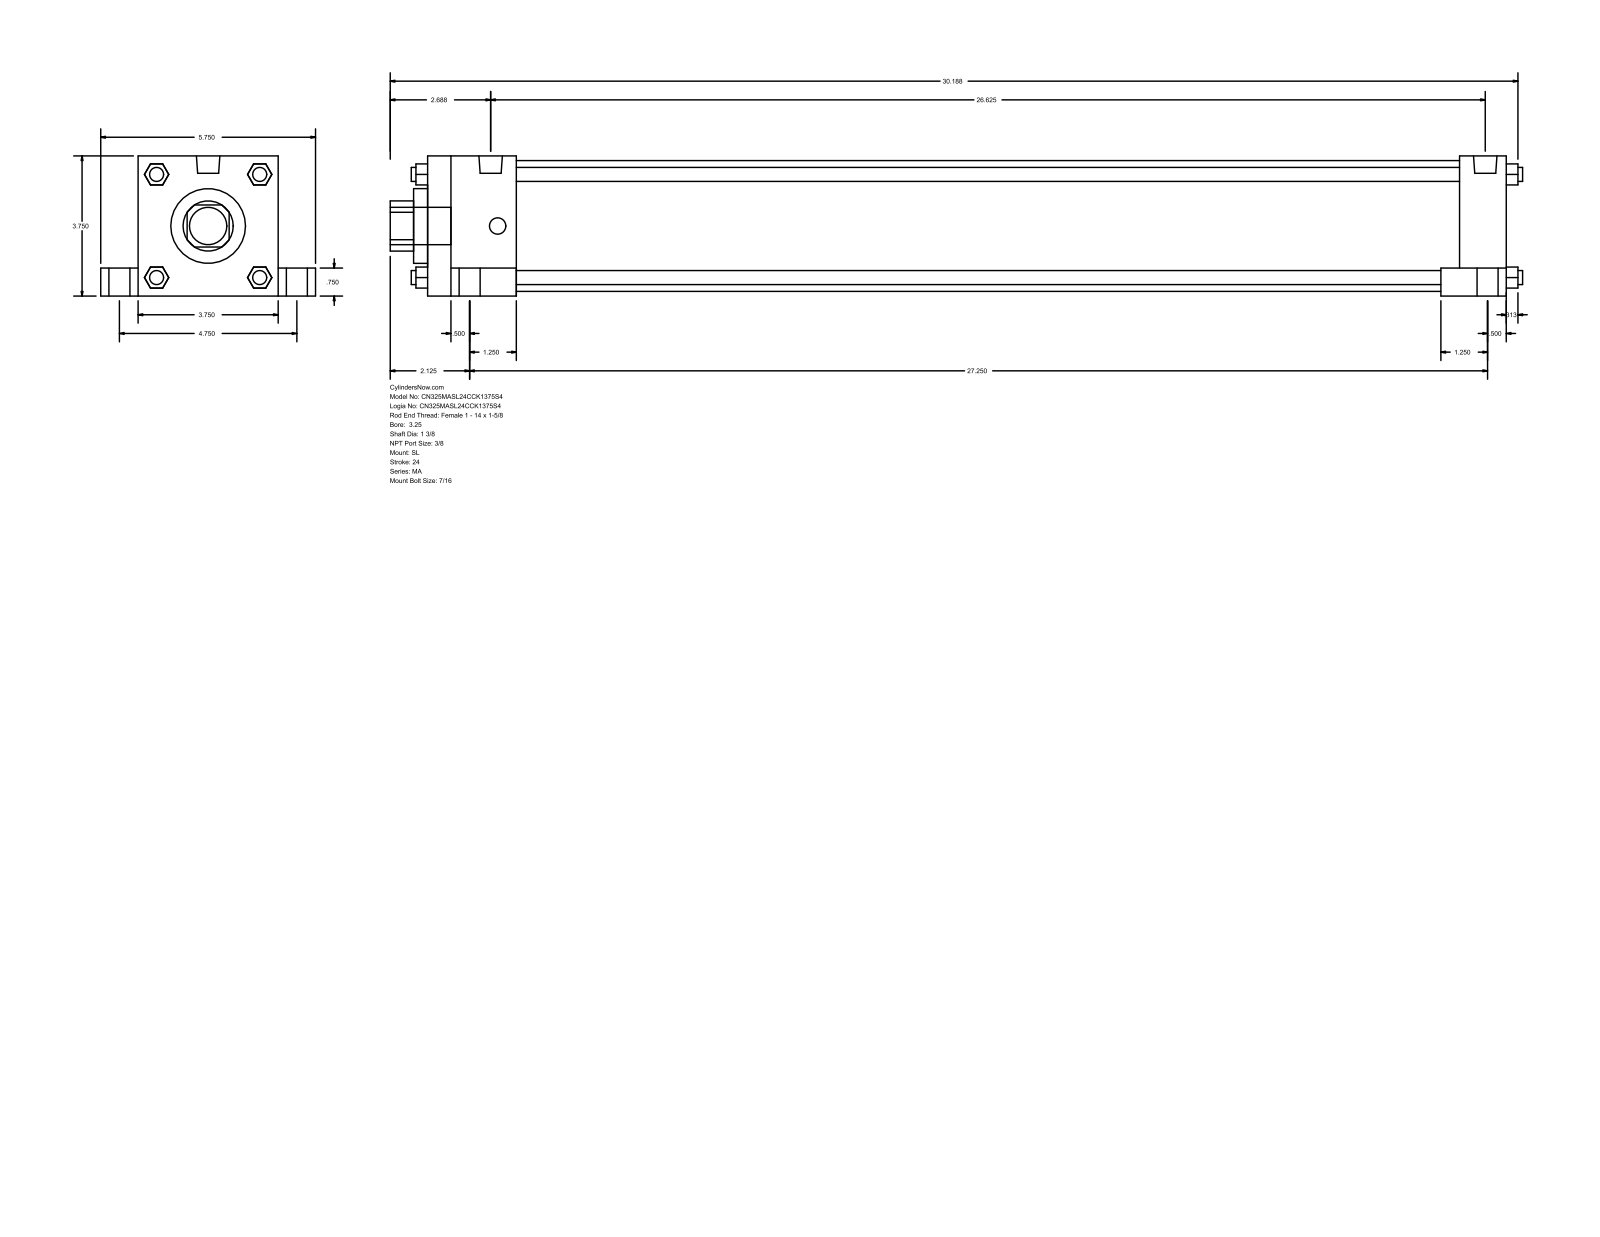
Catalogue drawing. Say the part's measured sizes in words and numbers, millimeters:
The part is named "MA_SL__0325_1.375". Its 3-D file was written by "GSSL Pune (CONFIG_CONTROL_DESIGN)". It is 0 solids with 148 faces: 112 planar, 36 cylindrical and 0 other. Overall it measures 769.94 by 146.05 by 95.25 millimeters. Round holes: 1 of diameter 34.92, 1 of diameter 50.8, 1 of diameter 88.9. Round bosses or shafts: 4 of diameter 20.64, 4 of diameter 14.29, 4 of diameter 11.11, 4 of diameter 9.53, 2 of diameter 15.93, 1 of diameter 25.4. Partial cylindrical surfaces (rounded edges, fillets, slot ends): 1 of radius 17.06. The main face-to-face distances are 95.24, 733.43, 25.41, 120.65, 701.68, 31.75, 60.32, 641.36, 673.11, 19.05.
